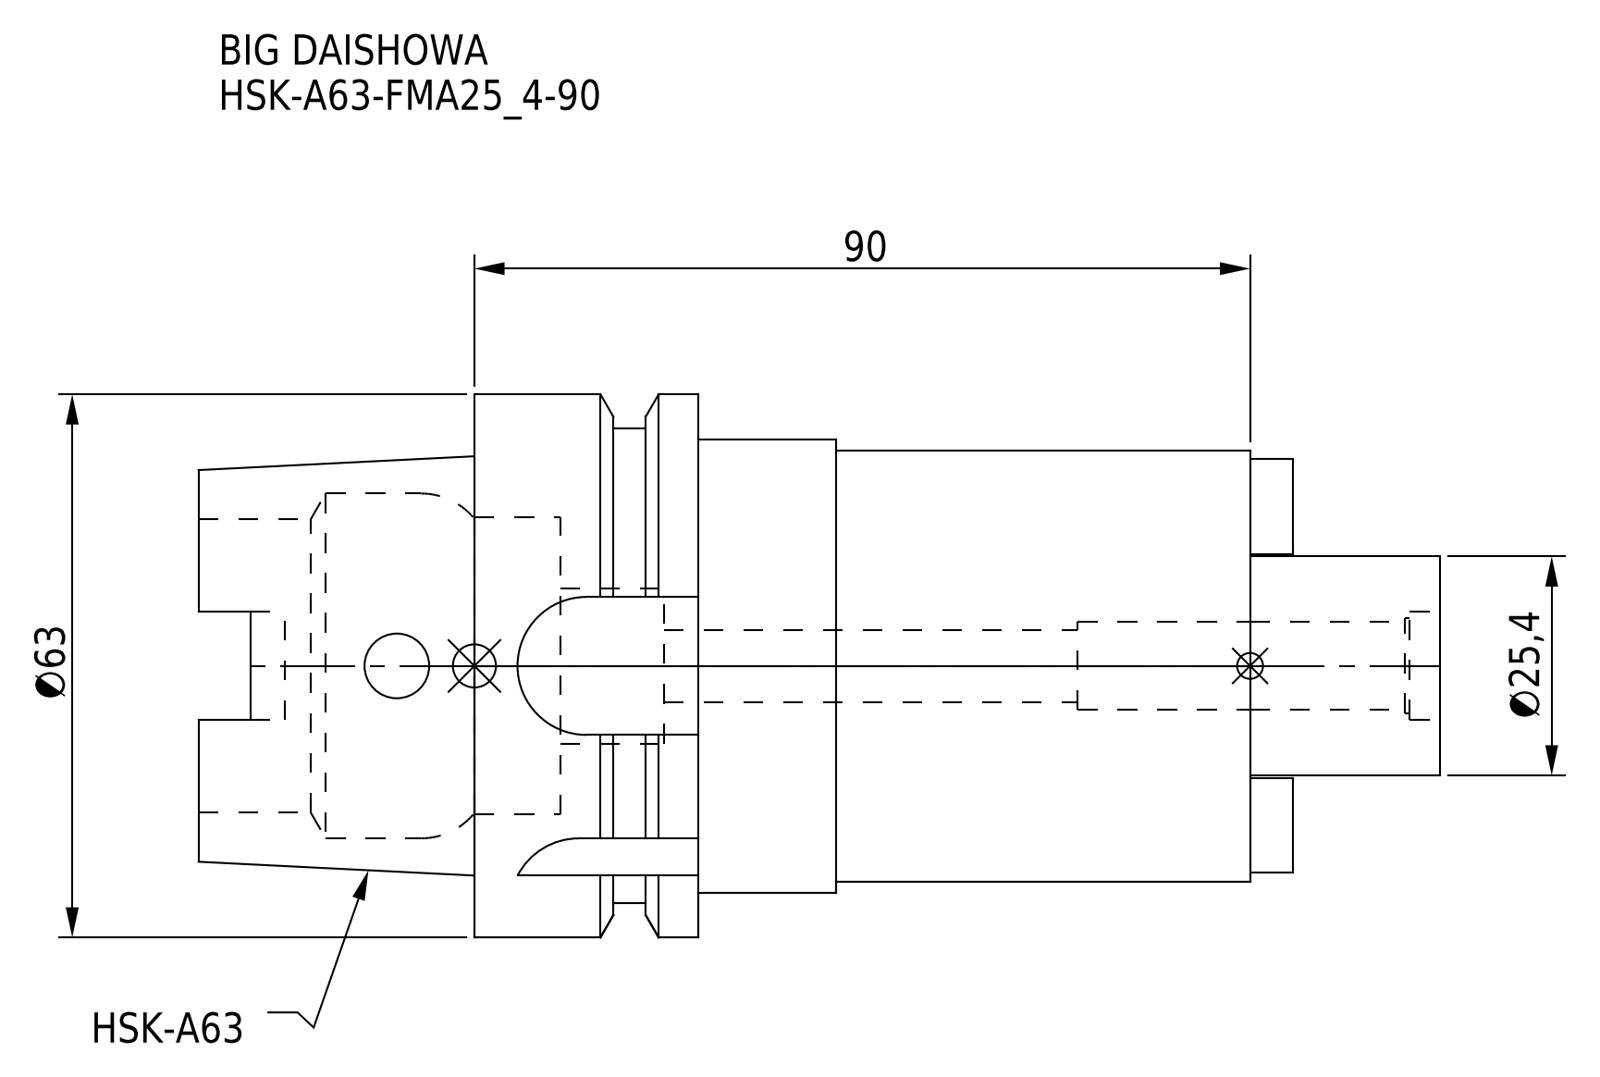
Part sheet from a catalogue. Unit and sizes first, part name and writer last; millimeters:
Units: millimetres
Overall size (bounding box): 144 × 63 × 63
Round holes (diameter × count): ⌀7.5 ×1, ⌀8.4 ×1, ⌀10.25 ×1, ⌀11 ×1, ⌀12.5 ×1, ⌀18 ×1, ⌀34 ×1, ⌀34.5 ×1, ⌀40 ×1
Round bosses / shafts (diameter × count): ⌀63 ×1, ⌀55 ×1, ⌀52.6 ×1, ⌀50 ×1, ⌀25.4 ×1
Partial cylindrical surfaces — rounded edges, fillets, slot ends (radius × count): R8 ×2, R9 ×1
Main face-to-face distances: 90, 26, 64, 80.05, 16.05, 9.95, 32, 122, 58, 41.95
Volume: 216 940 mm³ · Surface area: 37 328 mm²
Bodies: 1 solid, 98 faces (46 planar, 40 cylindrical, 12 other)
Part name (STEP PRODUCT): HSK-A63-FMA25_4-90
STEP written by: CREO PARAMETRIC BY PTC INC, 2016380 (AUTOMOTIVE_DESIGN)
